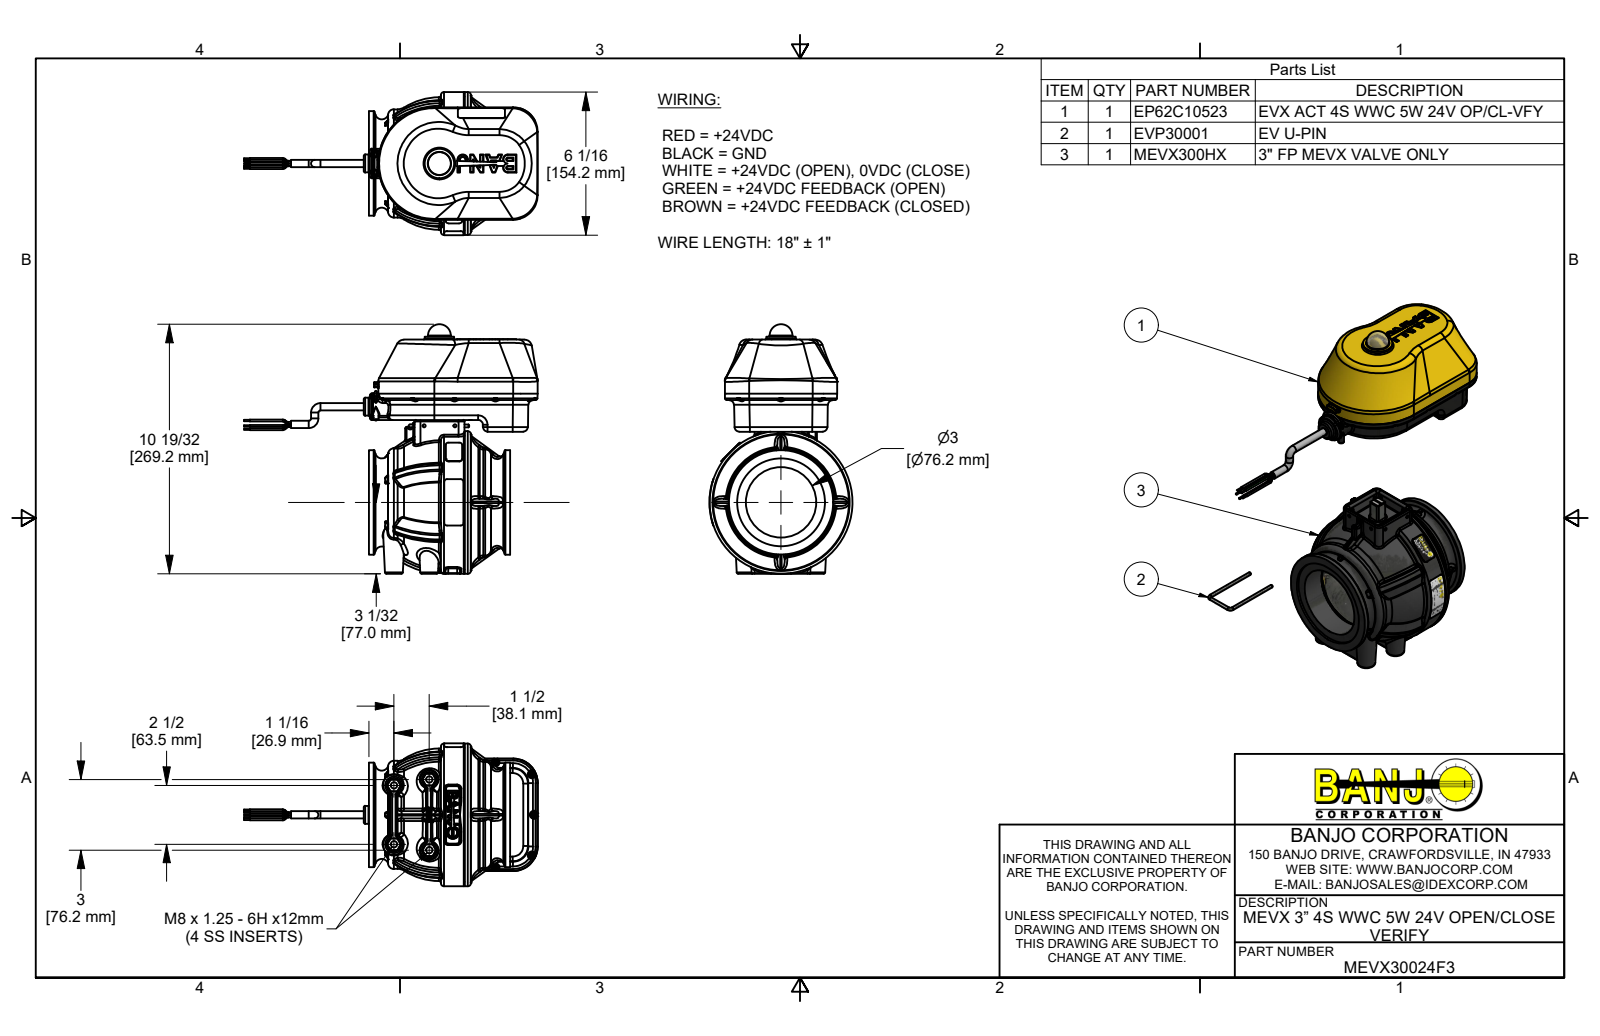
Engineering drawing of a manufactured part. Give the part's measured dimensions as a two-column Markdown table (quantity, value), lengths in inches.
| quantity | value |
| --- | --- |
| part name | MEVX30024F3; MEVX300HX; AQ206V; EVP30151 (+8 more) |
| STEP written by | Autodesk Inventor 2021 (AUTOMOTIVE_DESIGN) |
| units | inches |
| bodies | 81 solids, 8174 faces (2887 planar, 3134 cylindrical, 2153 other) |
| overall size | 12.476 × 10.6 × 6.072 |
| volume | 89.67 in³ |
| surface area | 901.7 in² |
| round holes (diameter × count) | 0.15 × 15, 0.095 × 11, 0.34 × 11, 0.08 × 7, 0.135 × 5, 0.104 × 4, 0.136 × 4, 0.148 × 4, 0.176 × 4, 0.262 × 4, 0.266 × 4, 0.433 × 4 |
| round bosses / shafts (diameter × count) | 0.08 × 25, 0.25 × 19, 0.14 × 11, 0.108 × 11, 0.085 × 11, 0.058 × 10, 0.437 × 4, 0.219 × 4 |
| partial cylindrical surfaces (radius × count) | 0.013 × 204, 0.405 × 138, 0.387 × 114, 0.309 × 112, 0.253 × 108, 0.609 × 106, 0.01 × 96, 0.04 × 46 |
| main face-to-face distances | 0.083, 0.5, 0.085, 0.125, 0.181, 0.096, 2.175, 2.356, 2.271, 0.1 |
| hole center spacings | 1.624, 2.309, 2.43, 2.754, 3.316, 0.998, 1.313, 1.468 |
